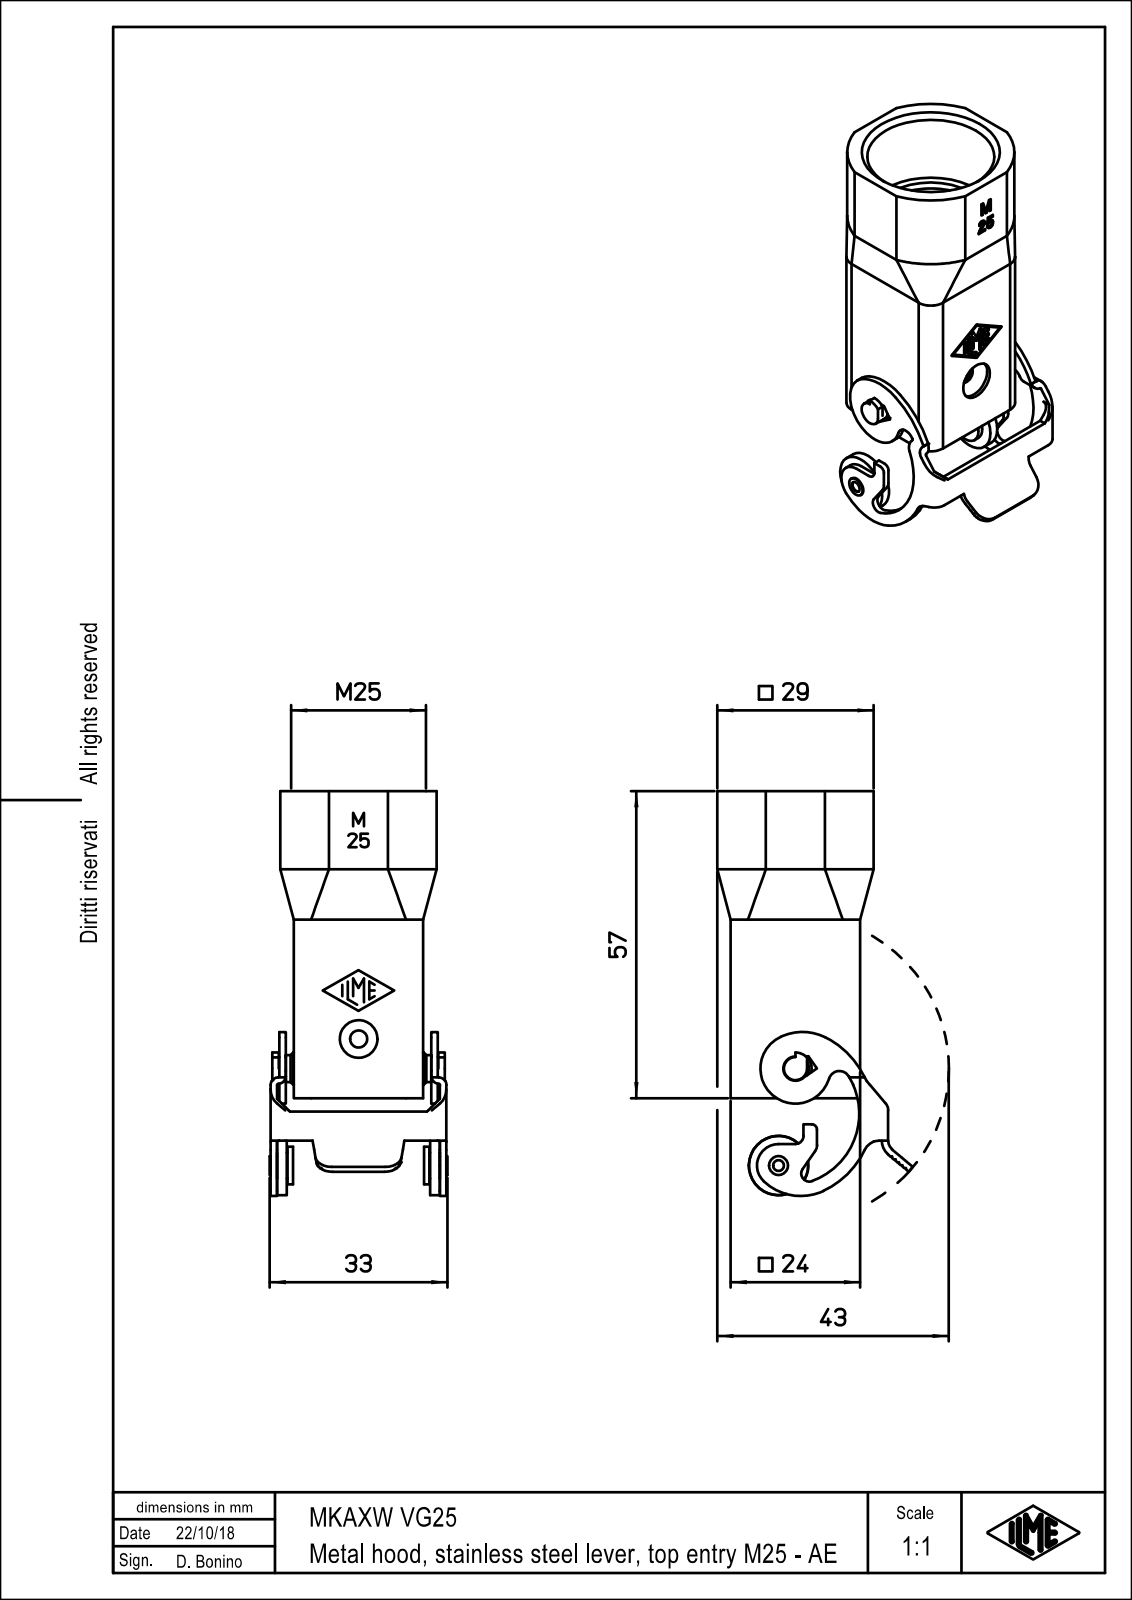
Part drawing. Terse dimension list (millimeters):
name: MKAXW_VG25
written by: PTC Creo Elements/Direct Modeling 19.0B 21-Mar-2015 (C) Parametric Technology GmbH (AUTOMOTIVE_DESIGN)
unit: mm
bodies: 1 solid, 377 faces (251 planar, 115 cylindrical, 11 other)
size: 66.13 × 40 × 33
volume: 10 927 mm³; area: 13 522 mm²
holes: 1× ⌀3.2, 1× ⌀7, 1× ⌀20, 1× ⌀25
bosses: 1× ⌀11, 1× ⌀7, 1× ⌀6, 1× ⌀5, 1× ⌀4.8, 1× ⌀4.3, 1× ⌀3.5
rounds: 15× R0.25, 8× R2, 5× R3.2, 4× R0.2, 4× R1.4, 4× R3, 3× R0.12, 2× R1.5
face distances: 1.2, 22.8, 21.6, 24, 25.3, 2.5, 3.7, 26.5, 2.7, 25.5
